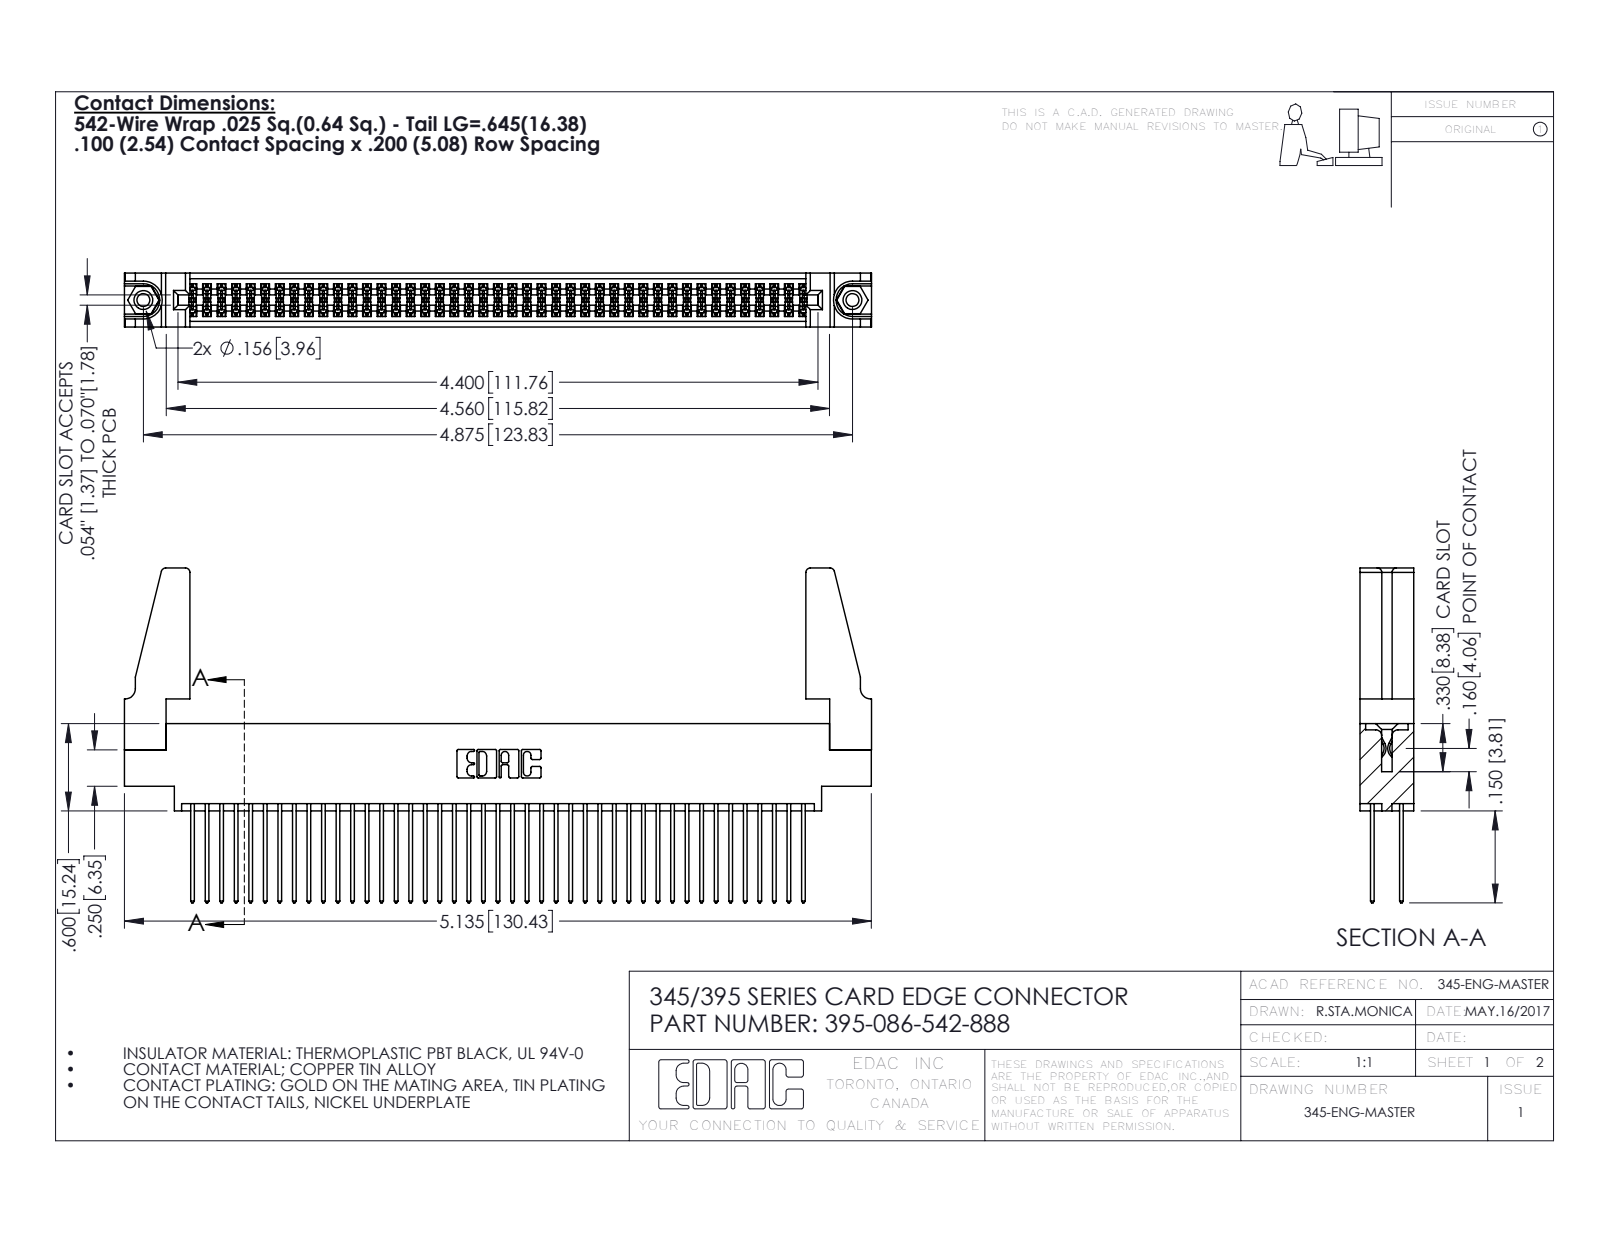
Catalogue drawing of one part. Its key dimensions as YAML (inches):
part_name: "345-292-001_345-293-142; 345-250-001_345-250-001-102; 345 Part_0.170 Offset - 0.156 Dia-TH; 345-220-078_345-220-088 (+1 more)"
step_written_by: "SolidWorks 2016 (CONFIG_CONTROL_DESIGN)"
units: inches
bodies: {solids: 91, faces: 4554, planar: 2994, cylindrical: 1544, other: 16}
overall_size: [5.136, 2.302, 0.37]
volume: 0.99
surface_area: 37.71
round_holes:
  - {diameter: 0.089, count: 2}
  - {diameter: 0.125, count: 2}
  - {diameter: 0.156, count: 2}
  - {diameter: 0.064, count: 1}
round_bosses_or_shafts:
  - {diameter: 0.155, count: 2}
partial_cylinders:
  - {radius: 0.006, count: 129}
  - {radius: 0.01, count: 86}
  - {radius: 0.01, count: 22}
  - {radius: 0.03, count: 8}
  - {radius: 0.007, count: 6}
  - {radius: 0.031, count: 6}
  - {radius: 0.026, count: 3}
  - {radius: 0.014, count: 2}
face_to_face_distances: [0.072, 0.298, 0.37, 0.2, 0.098, 0.272, 0.025, 0.225, 0.175, 0.149]
hole_center_spacings: [0.27, 4.639, 4.875]
